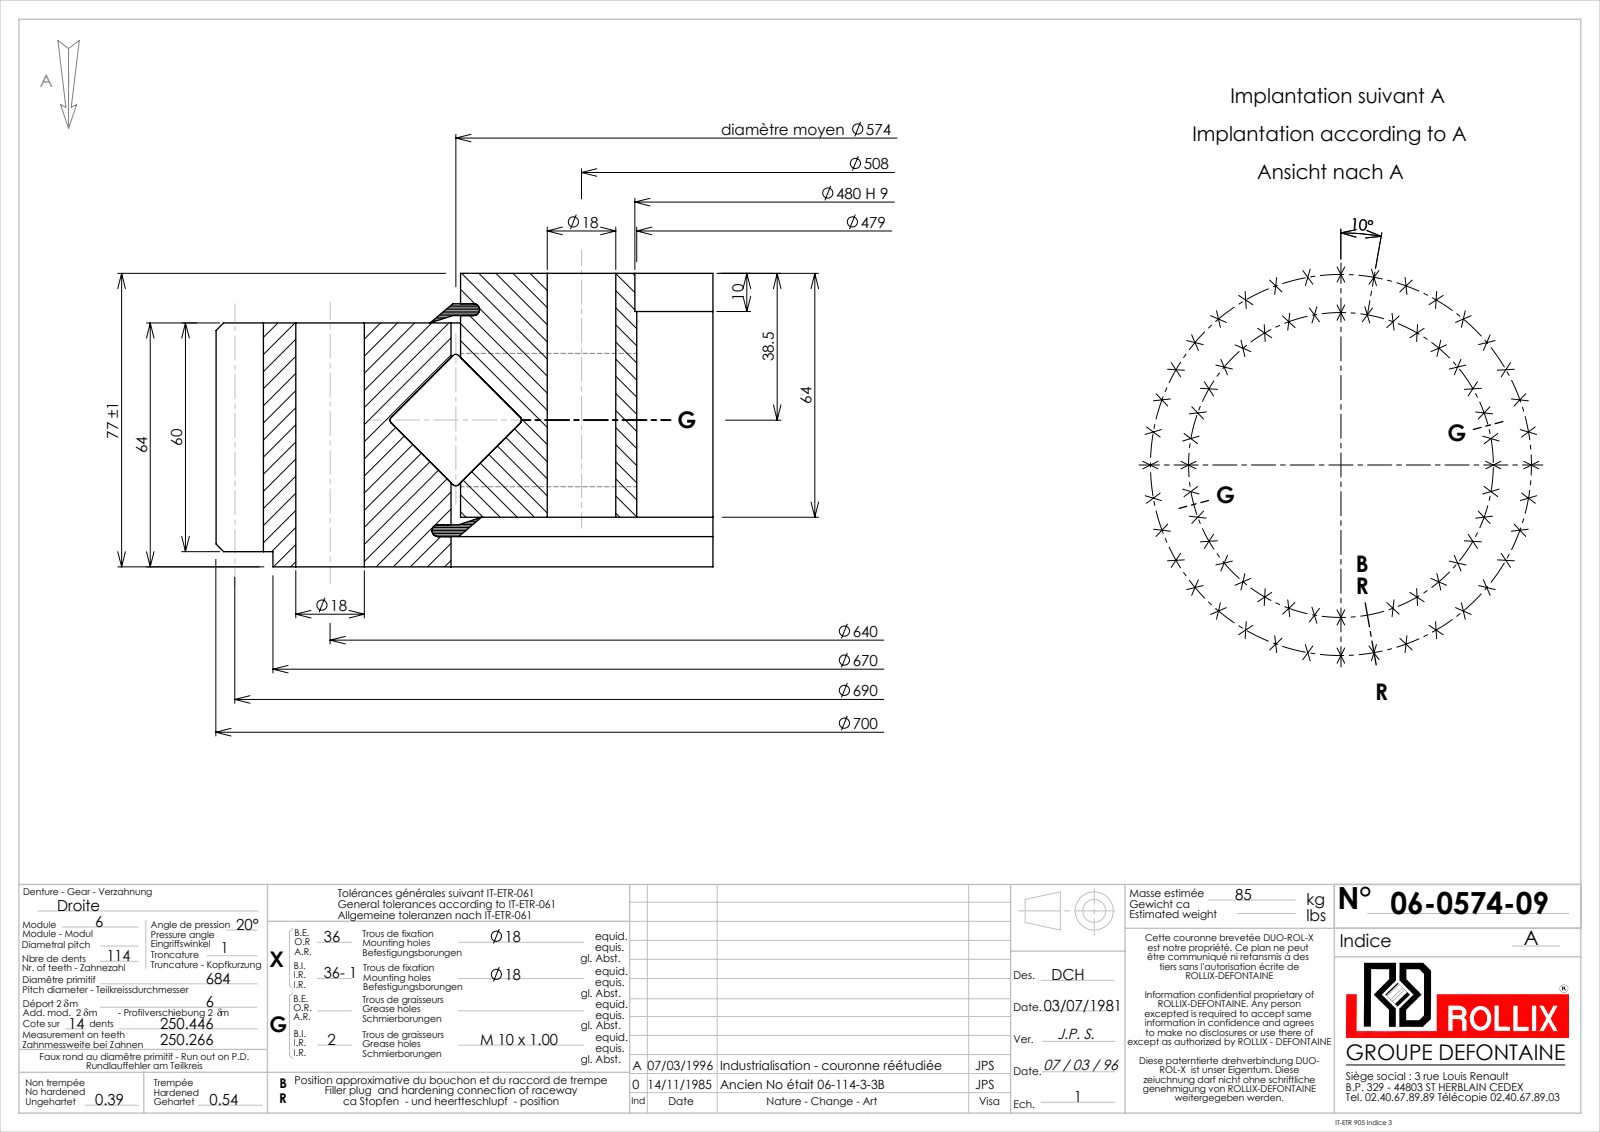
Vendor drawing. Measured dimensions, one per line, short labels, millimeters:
name: 06-0574-09
written by: SolidWorks 2016 (CONFIG_CONTROL_DESIGN)
unit: mm
bodies: 5 solids, 907 faces (244 planar, 395 cylindrical, 268 other)
size: 700 × 699.88 × 77
volume: 9 869 000 mm³; area: 1 372 000 mm²
holes: 71× ⌀18, 2× ⌀9, 1× ⌀479, 1× ⌀480, 1× ⌀576.5
bosses: 1× ⌀670, 1× ⌀571.5, 1× ⌀25
rounds: 1× R337.5, 1× R350
face distances: 64, 13, 51, 77, 11.05, 65.95, 1.95, 52.95, 7.95, 69.05
hole spacings: 320, 367.09, 55.78, 490.27, 618.19, 111.13, 165.64, 411.38
